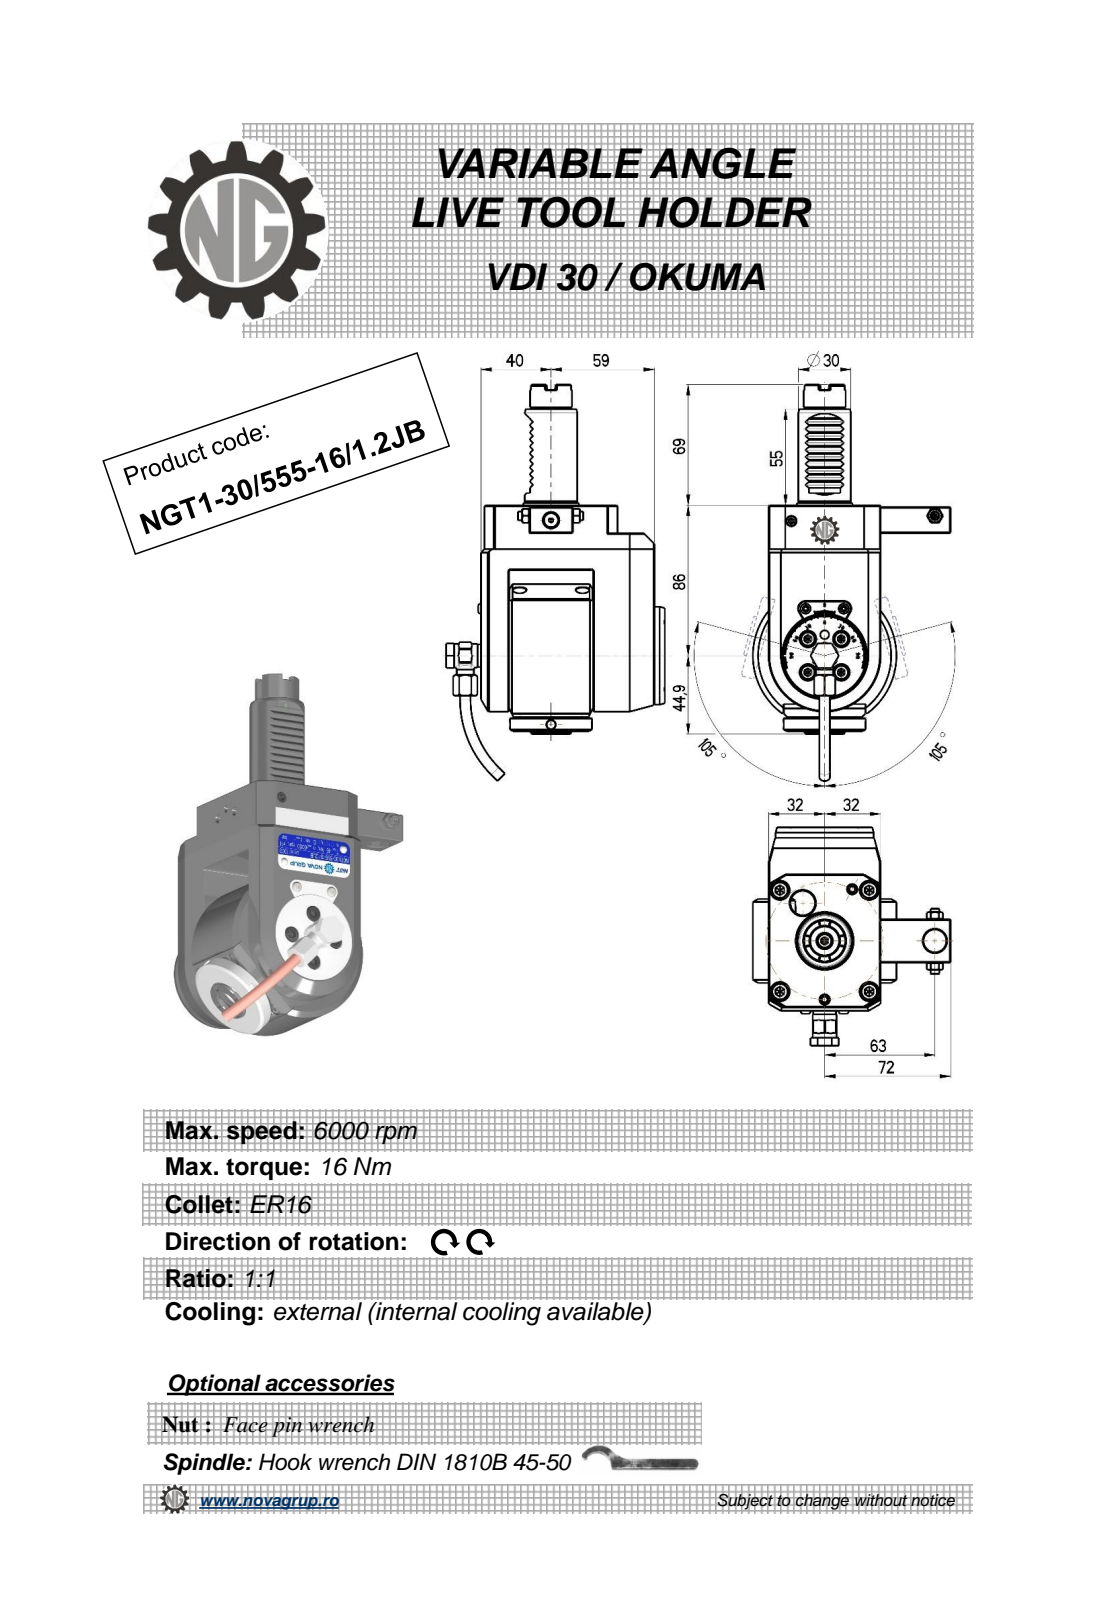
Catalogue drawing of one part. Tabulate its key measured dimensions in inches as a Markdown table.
| quantity | value |
| --- | --- |
| part name | NGT1_30_555_16_1_2JB |
| STEP written by | PRO/ENGINEER BY PARAMETRIC TECHNOLOGY CORPORATION, 2010280 (CONFIG_CONTROL_DESIGN) |
| units | inches |
| bodies | 1 solid, 561 faces (233 planar, 144 cylindrical, 184 other) |
| overall size | 8.924 × 4.917 × 4.449 |
| volume | 46.99 in³ |
| surface area | 116.8 in² |
| round holes (diameter × count) | 0.126 × 4, 0.157 × 3, 0.197 × 2, 0.118 × 1, 0.165 × 1, 0.244 × 1, 0.354 × 1, 0.374 × 1, 0.433 × 1, 0.492 × 1, 0.512 × 1, 0.669 × 1 |
| round bosses / shafts (diameter × count) | 0.394 × 2, 0.236 × 2, 0.224 × 2, 3.228 × 1, 2.205 × 1, 1.85 × 1, 1.417 × 1, 1.181 × 1 |
| partial cylindrical surfaces (radius × count) | 0.01 × 12, 0.012 × 10, 0.006 × 6, 0.02 × 4, 0.039 × 2, 0.303 × 1, 1.26 × 1 |
| main face-to-face distances | 2.52, 0.63, 1.457, 0.827, 3.898, 0.236, 4.134, 0.551, 1.378, 1.614 |
| hole center spacings | 0.364, 0.515, 0.728, 1.963, 1.979, 2.507, 0.016, 1.553 |
